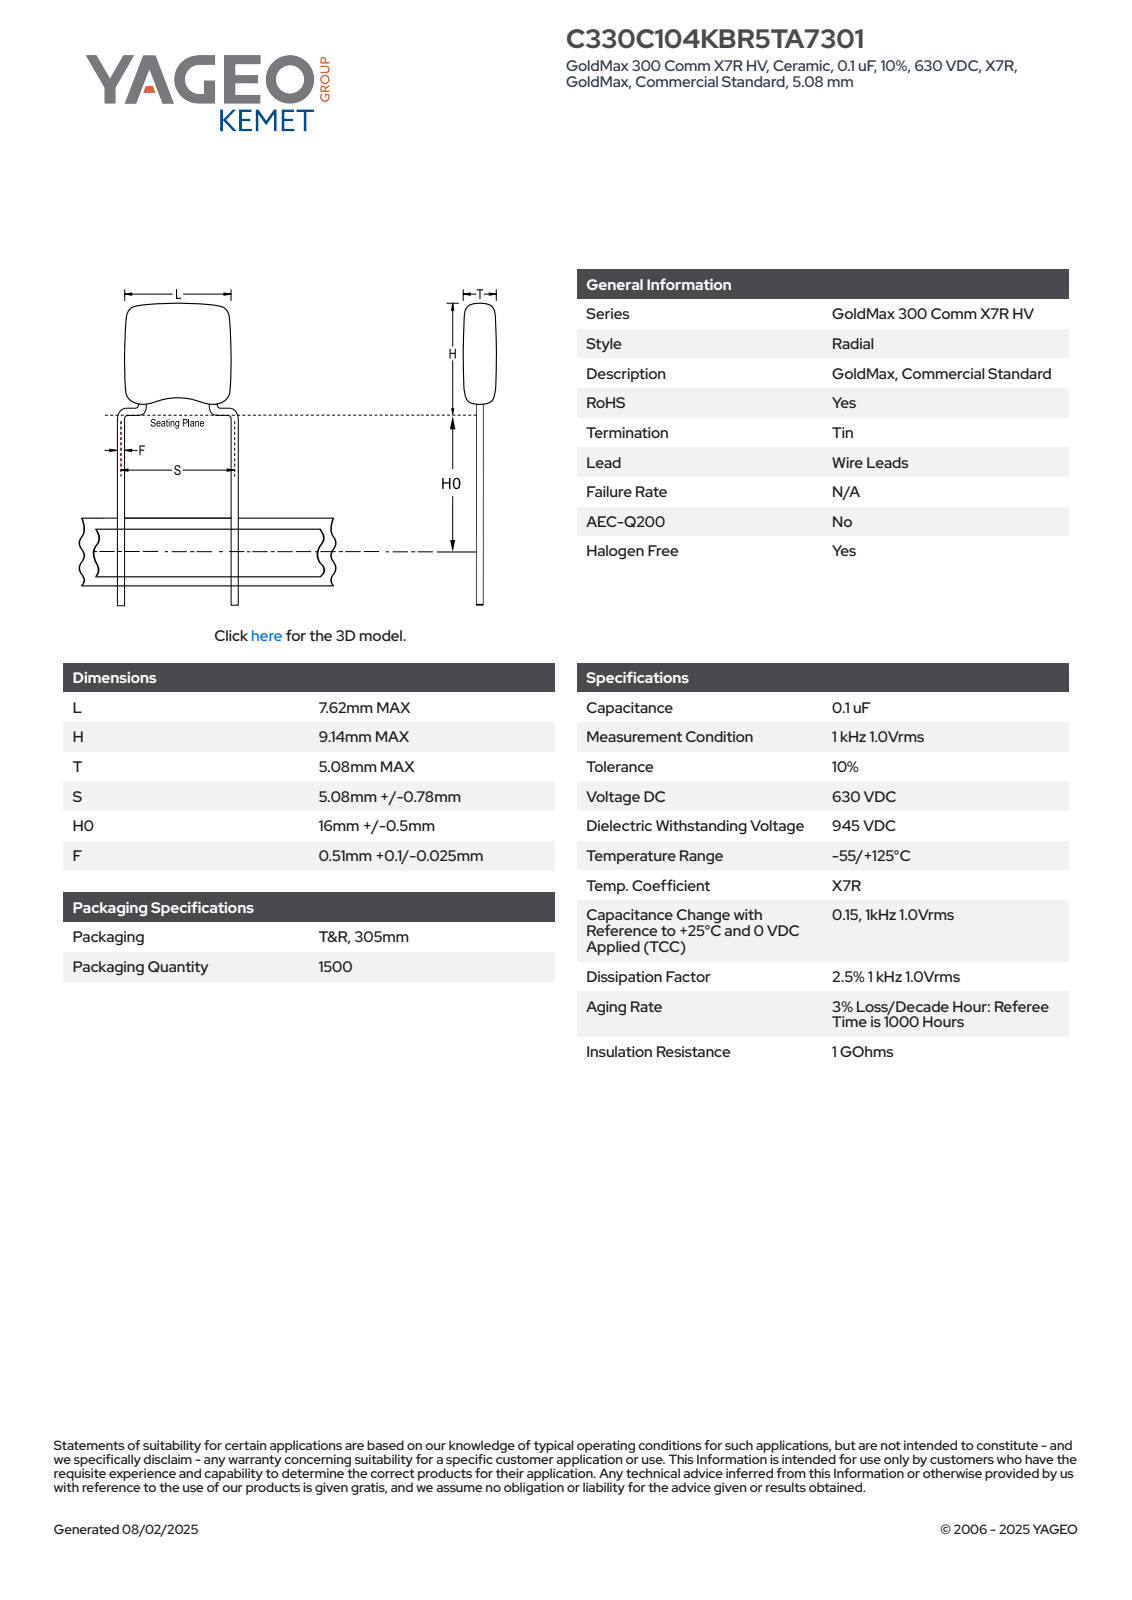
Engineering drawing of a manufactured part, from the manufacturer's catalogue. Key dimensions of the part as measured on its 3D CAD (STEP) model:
Part name (STEP PRODUCT): CCR_SB_7.62X9.14_L7.62H9.14T5.08S5.08H016.5F0.51
STEP written by: SolidWorks 2014 (AUTOMOTIVE_DESIGN)
Units: millimetres
Bodies: 4 solids, 97 faces (65 planar, 14 cylindrical, 18 other)
Overall size (bounding box): 25.64 × 7.62 × 5.08
Volume: 273 mm³ · Surface area: 293 mm²
Round bosses / shafts (diameter × count): ⌀0.51 ×2
Partial cylindrical surfaces — rounded edges, fillets, slot ends (radius × count): R1 ×10
Main face-to-face distances: 5.08, 7.62, 7.22, 3.9, 3.32, 3.26, 0.64, 3.96, 0.58, 0.52
